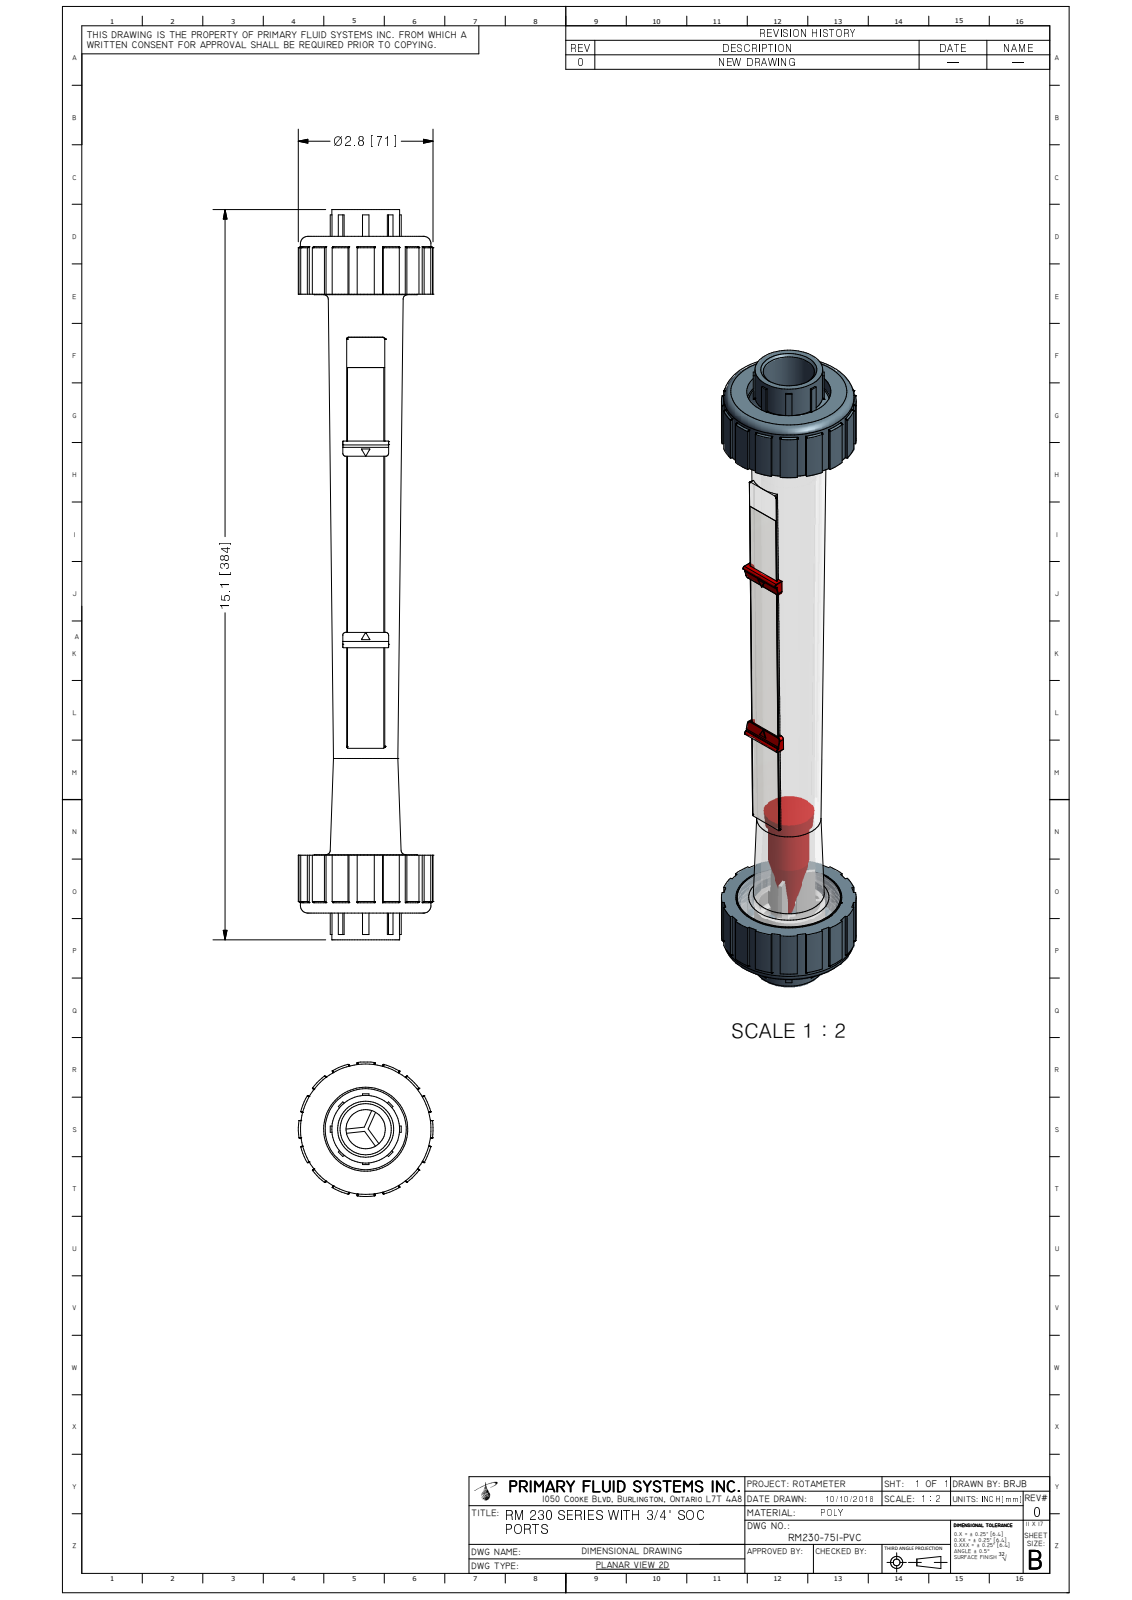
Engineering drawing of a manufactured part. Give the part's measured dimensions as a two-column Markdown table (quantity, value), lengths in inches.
| quantity | value |
| --- | --- |
| part name | RM230-75I-PVC_R0 |
| STEP written by | Autodesk Inventor 2009 (AUTOMOTIVE_DESIGN) |
| units | inches |
| bodies | 1 solid, 587 faces (262 planar, 126 cylindrical, 199 other) |
| overall size | 15.1 × 2.783 × 2.783 |
| volume | 31.99 in³ |
| surface area | 168.3 in² |
| round holes (diameter × count) | 1.058 × 1, 1.738 × 1, 2.19 × 1 |
| round bosses / shafts (diameter × count) | 2.697 × 1, 2.152 × 1, 2.026 × 1, 1.485 × 1, 1.4 × 1 |
| partial cylindrical surfaces (radius × count) | 0.008 × 18, 0.01 × 16, 0.004 × 10, 0.006 × 4, 0.06 × 4, 0.008 × 2, 0.04 × 2, 0.045 × 2 |
| main face-to-face distances | 1.197, 12.795, 1.205, 12.787, 11.59, 0.496, 13.496, 0.701, 12.299, 12.291 |
